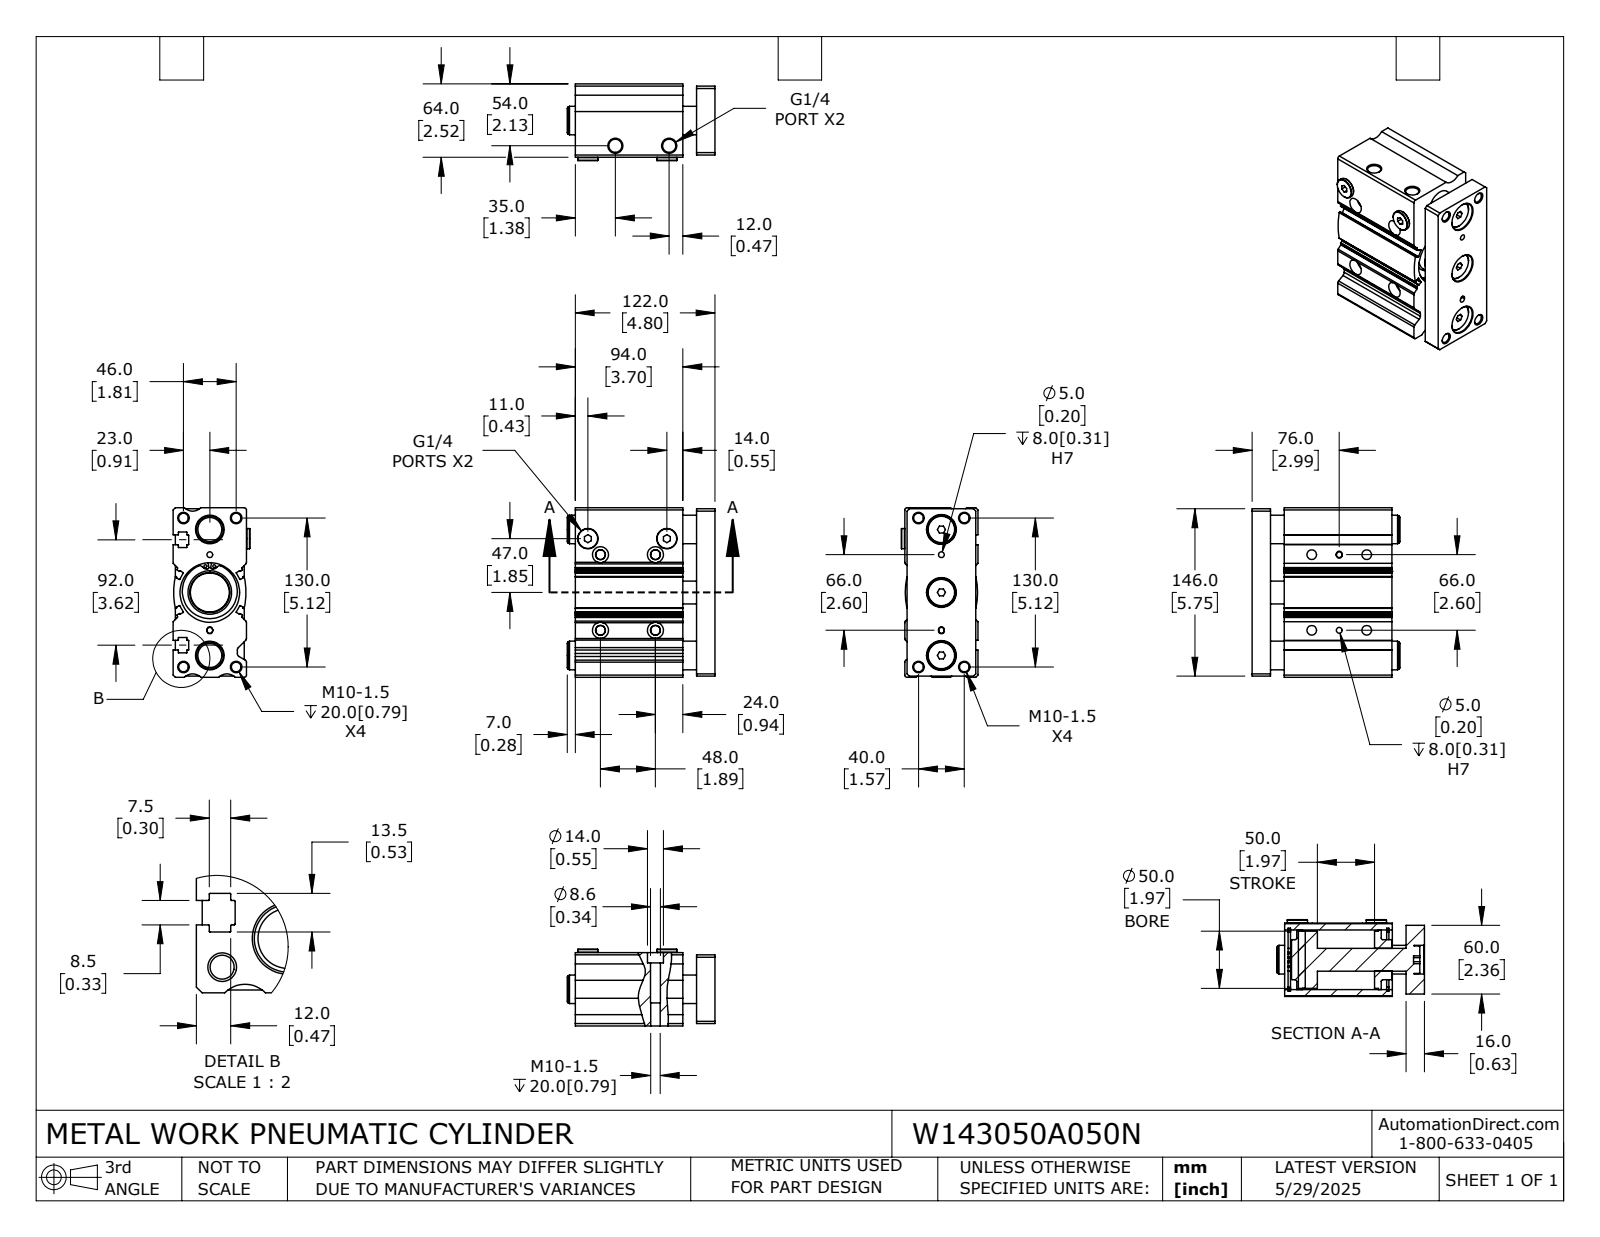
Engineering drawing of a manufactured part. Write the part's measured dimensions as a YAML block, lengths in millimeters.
part_name: "W143050A050N_ROD; W143050A050N; W143050A050N_BODY"
step_written_by: "SolidWorks 2024 (CONFIG_CONTROL_DESIGN)"
units: millimeters
bodies: {solids: 6, faces: 466, planar: 186, cylindrical: 224, other: 56}
overall_size: [148, 129, 67]
volume: 833000
surface_area: 178300
round_holes:
  - {diameter: 8.4, count: 12}
  - {diameter: 2.5, count: 4}
  - {diameter: 5, count: 4}
  - {diameter: 8.6, count: 4}
  - {diameter: 14, count: 4}
  - {diameter: 25, count: 3}
  - {diameter: 11.5, count: 2}
  - {diameter: 48, count: 2}
  - {diameter: 20, count: 1}
round_bosses_or_shafts:
  - {diameter: 24, count: 3}
  - {diameter: 17.7, count: 2}
  - {diameter: 55, count: 1}
  - {diameter: 52, count: 1}
  - {diameter: 50, count: 1}
  - {diameter: 35, count: 1}
partial_cylinders:
  - {radius: 0.3, count: 44}
  - {radius: 0.5, count: 12}
  - {radius: 3, count: 10}
  - {radius: 2, count: 6}
  - {radius: 68, count: 6}
  - {radius: 1, count: 4}
  - {radius: 2.5, count: 4}
  - {radius: 10, count: 3}
face_to_face_distances: [12, 94, 16, 106, 2, 28, 64, 122, 62, 6]
hole_center_spacings: [3, 10.8, 22.1, 22.4, 23.3, 24, 24.5, 25.1]
